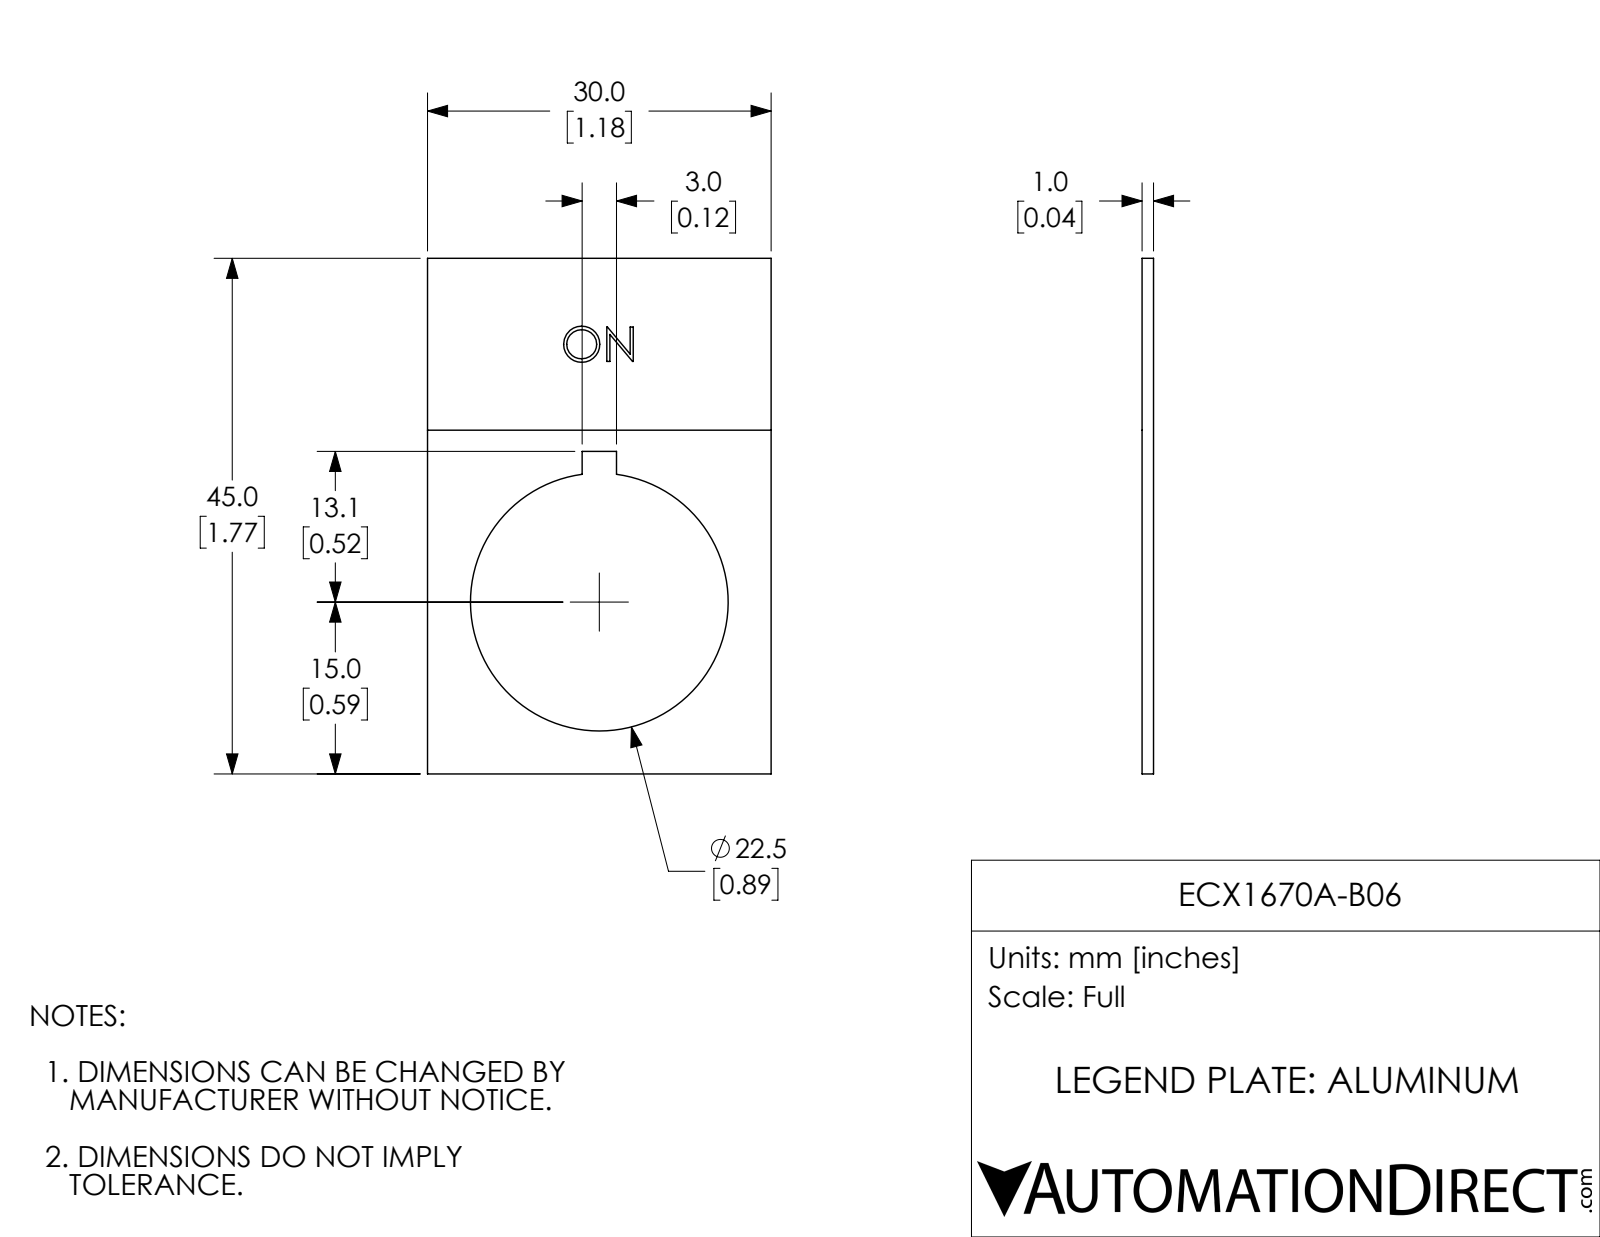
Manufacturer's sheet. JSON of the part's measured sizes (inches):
{"part_name": "ECX1670A-B06", "step_written_by": "SolidWorks 2017 (AUTOMOTIVE_DESIGN)", "units": "inches", "bodies": {"solids": 1, "faces": 34, "planar": 23, "cylindrical": 3, "other": 8}, "overall_size": [1.772, 1.181, 0.039], "volume_in3": 0.058, "surface_area_in2": 3.284, "round_holes": [[0.886, 1]], "face_to_face_distances": [0.039, 1.181, 1.772, 0.038, 0.531, 0.65, 1.108, 0.663, 0.118, 0.08]}
